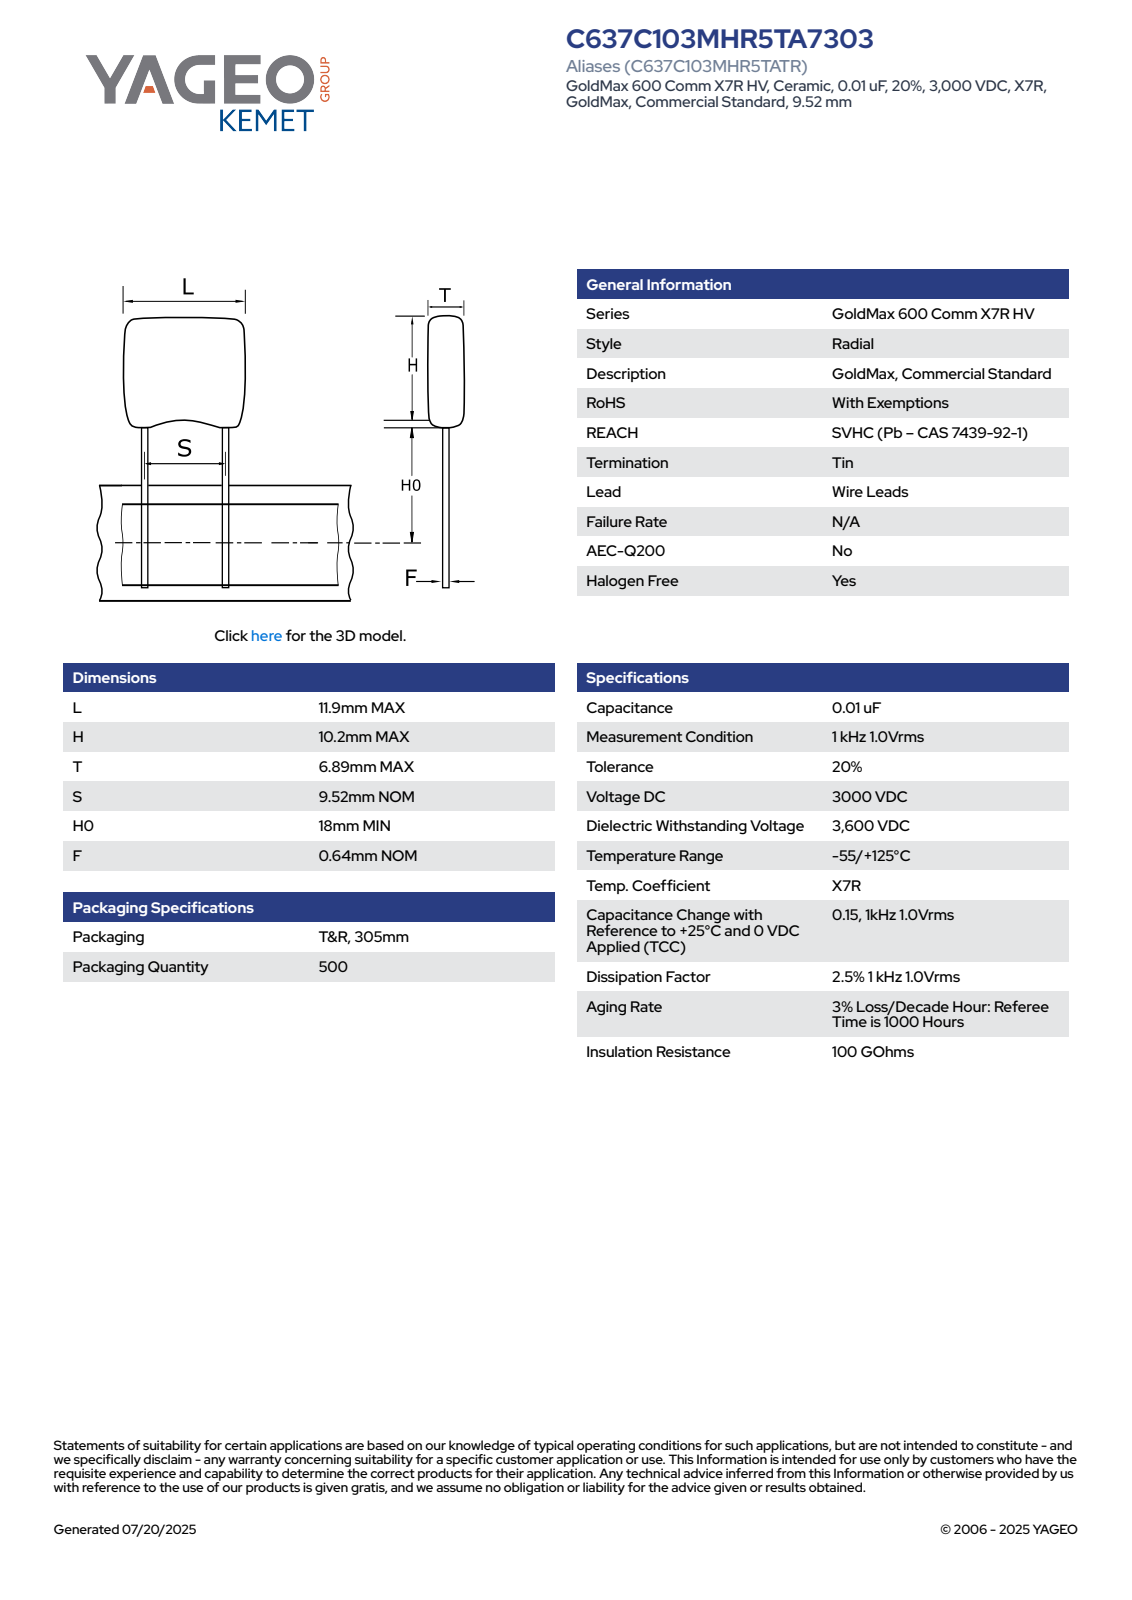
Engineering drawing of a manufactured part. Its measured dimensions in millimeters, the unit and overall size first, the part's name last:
Units: millimetres
Overall size (bounding box): 29.36 × 11.9 × 6.89
Round bosses / shafts (diameter × count): ⌀0.64 ×2
Partial cylindrical surfaces — rounded edges, fillets, slot ends (radius × count): R0.75 ×10
Main face-to-face distances: 6.89, 11.9, 11.36, 18, 29.36, 5.05, 6.31, 24.31, 23.05, 1.26
Volume: 931 mm³ · Surface area: 638 mm²
Bodies: 4 solids, 83 faces (65 planar, 14 cylindrical, 4 other)
Part name (STEP PRODUCT): CCR_KRCST_11.9X10.2_L11.9H10.2T6.89S9.52H018F0.64
STEP written by: SolidWorks 2014 (AUTOMOTIVE_DESIGN)
